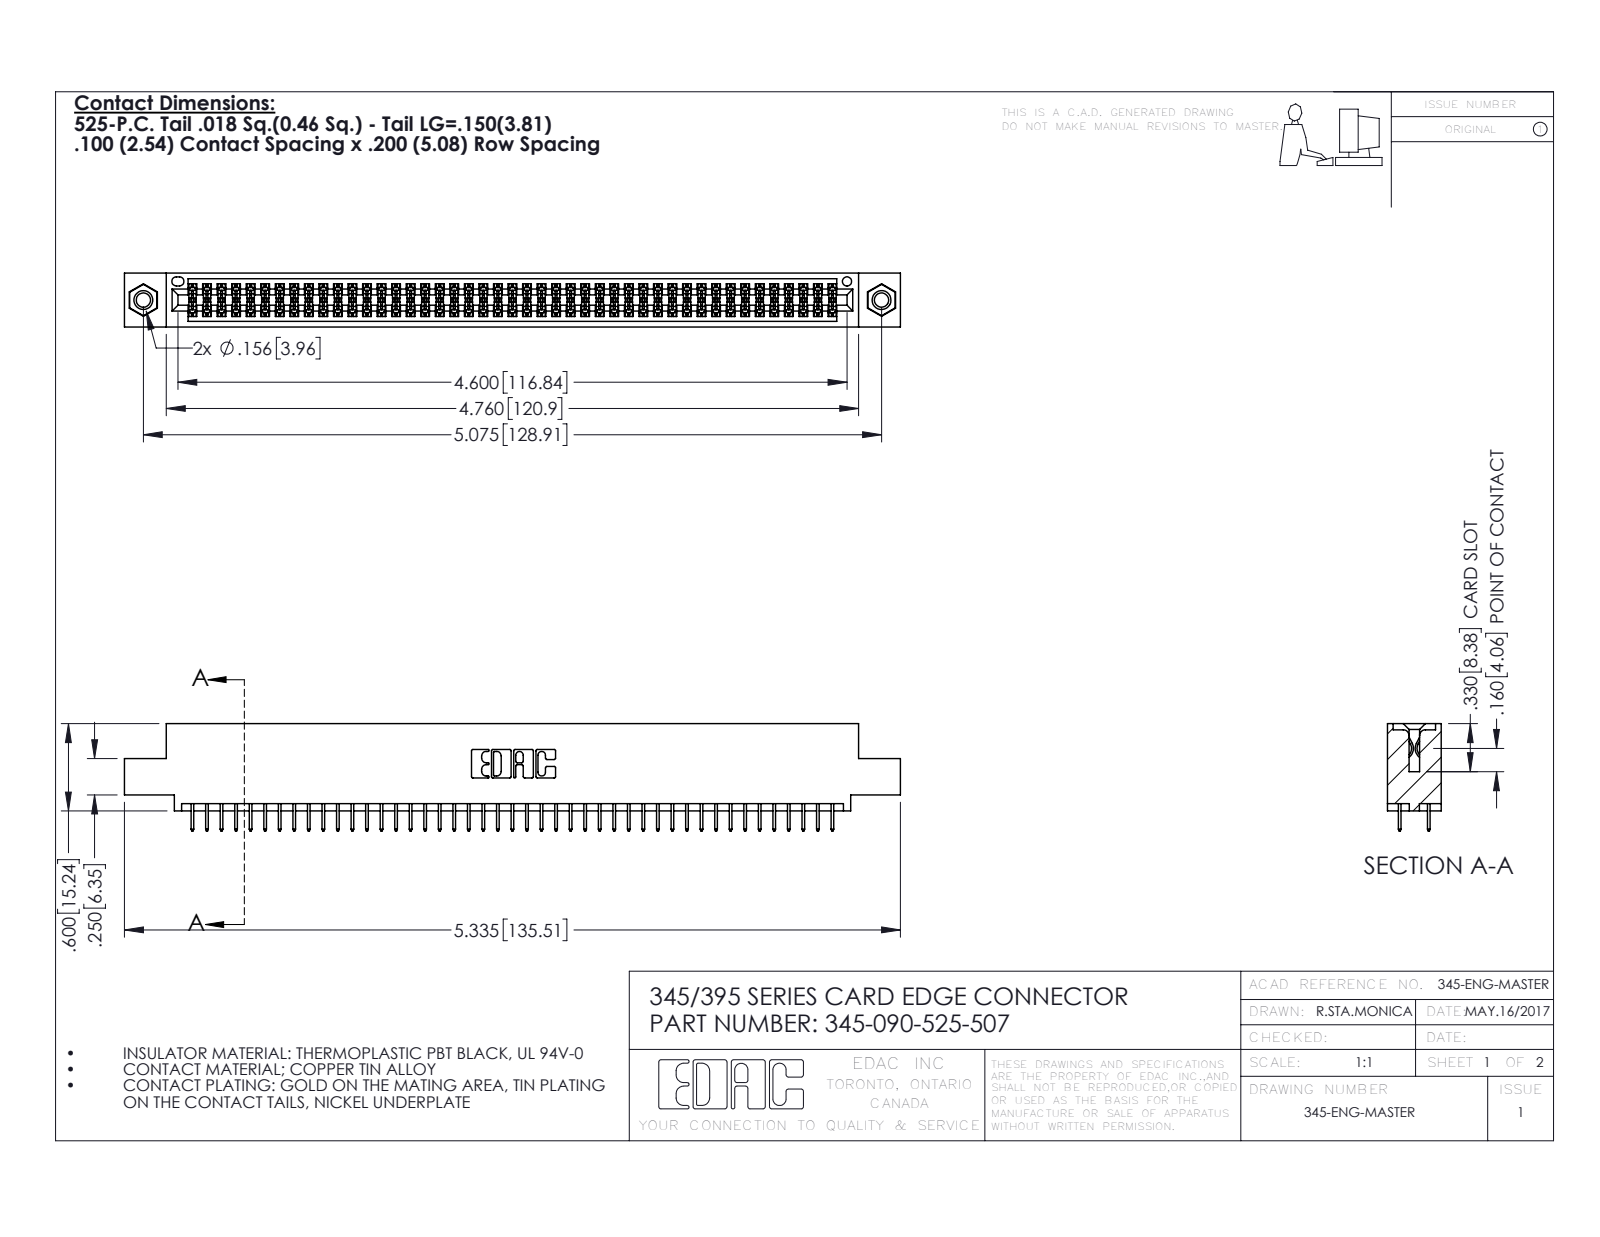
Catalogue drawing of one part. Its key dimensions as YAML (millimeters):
part_name: "345 Part_0.110 Offset - 0.156 Dia-TI; 345-090-525-507; 345-250-001_345-250-005-103; 345-292-001_345-293-125"
step_written_by: "SolidWorks 2020 (CONFIG_CONTROL_DESIGN)"
units: millimeters
bodies: {solids: 93, faces: 5050, planar: 3626, cylindrical: 1408, other: 16}
overall_size: [135.5, 18.7, 9.4]
volume: 13000
surface_area: 18880
round_holes:
  - {diameter: 2.5, count: 2}
  - {diameter: 3.2, count: 2}
  - {diameter: 4, count: 2}
  - {diameter: 1.6, count: 1}
round_bosses_or_shafts:
  - {diameter: 3.9, count: 2}
partial_cylinders:
  - {radius: 0.2, count: 180}
  - {radius: 0.3, count: 22}
  - {radius: 0.2, count: 6}
  - {radius: 0.8, count: 6}
  - {radius: 0.7, count: 3}
  - {radius: 0.4, count: 2}
  - {radius: 0.5, count: 2}
  - {radius: 0.6, count: 2}
face_to_face_distances: [1.8, 7.6, 5.1, 9.4, 2.5, 6.9, 0.6, 5.7, 1.8, 4.4]
hole_center_spacings: [6.9, 122.9, 128.9]
